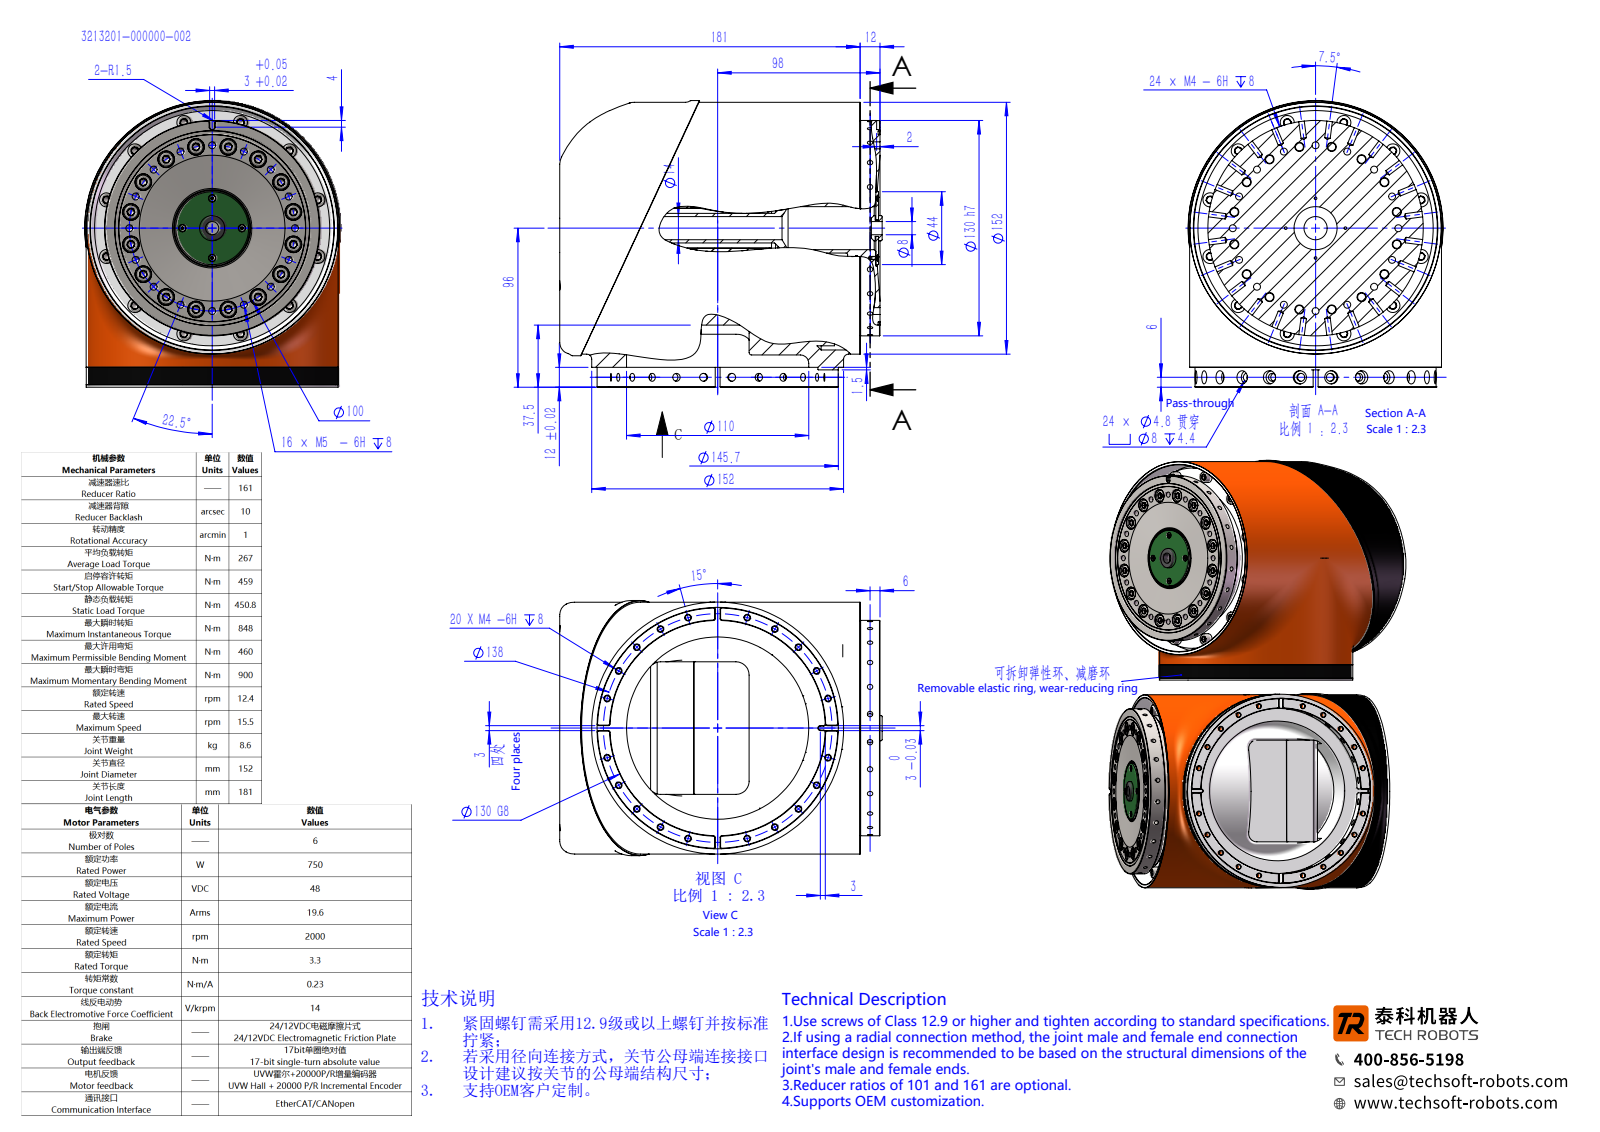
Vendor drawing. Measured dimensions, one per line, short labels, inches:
written by: SolidWorks 2016 (CONFIG_CONTROL_DESIGN)
unit: in
bodies: 15 solids, 1873 faces (617 planar, 548 cylindrical, 708 other)
size: 7.765 × 6.811 × 6.063
volume: 209 in³; area: 357.5 in²
holes: 46× ⌀0.13, 28× ⌀0.165, 25× ⌀0.315, 24× ⌀0.189, 17× ⌀0.394, 16× ⌀0.217, 4× ⌀0.063, 4× ⌀0.094, 3× ⌀0.134, 3× ⌀0.276, 1× ⌀0.551, 1× ⌀1.024
bosses: 28× ⌀0.335, 24× ⌀0.19, 4× ⌀0.138, 4× ⌀0.079, 1× ⌀6.063, 1× ⌀5.988, 1× ⌀5.984, 1× ⌀5.736
rounds: 18× R0.039, 6× R0.059, 4× R0.315, 2× R0.394, 1× R2.988, 1× R3.012
face distances: 6.528, 0.472, 1.004, 7.61, 1.083, 7.138, 0.61, 1.476, 7.512, 0.984
hole spacings: 2.717, 1.507, 1.856, 1.969, 3.043, 3.637, 2.784, 1.406
